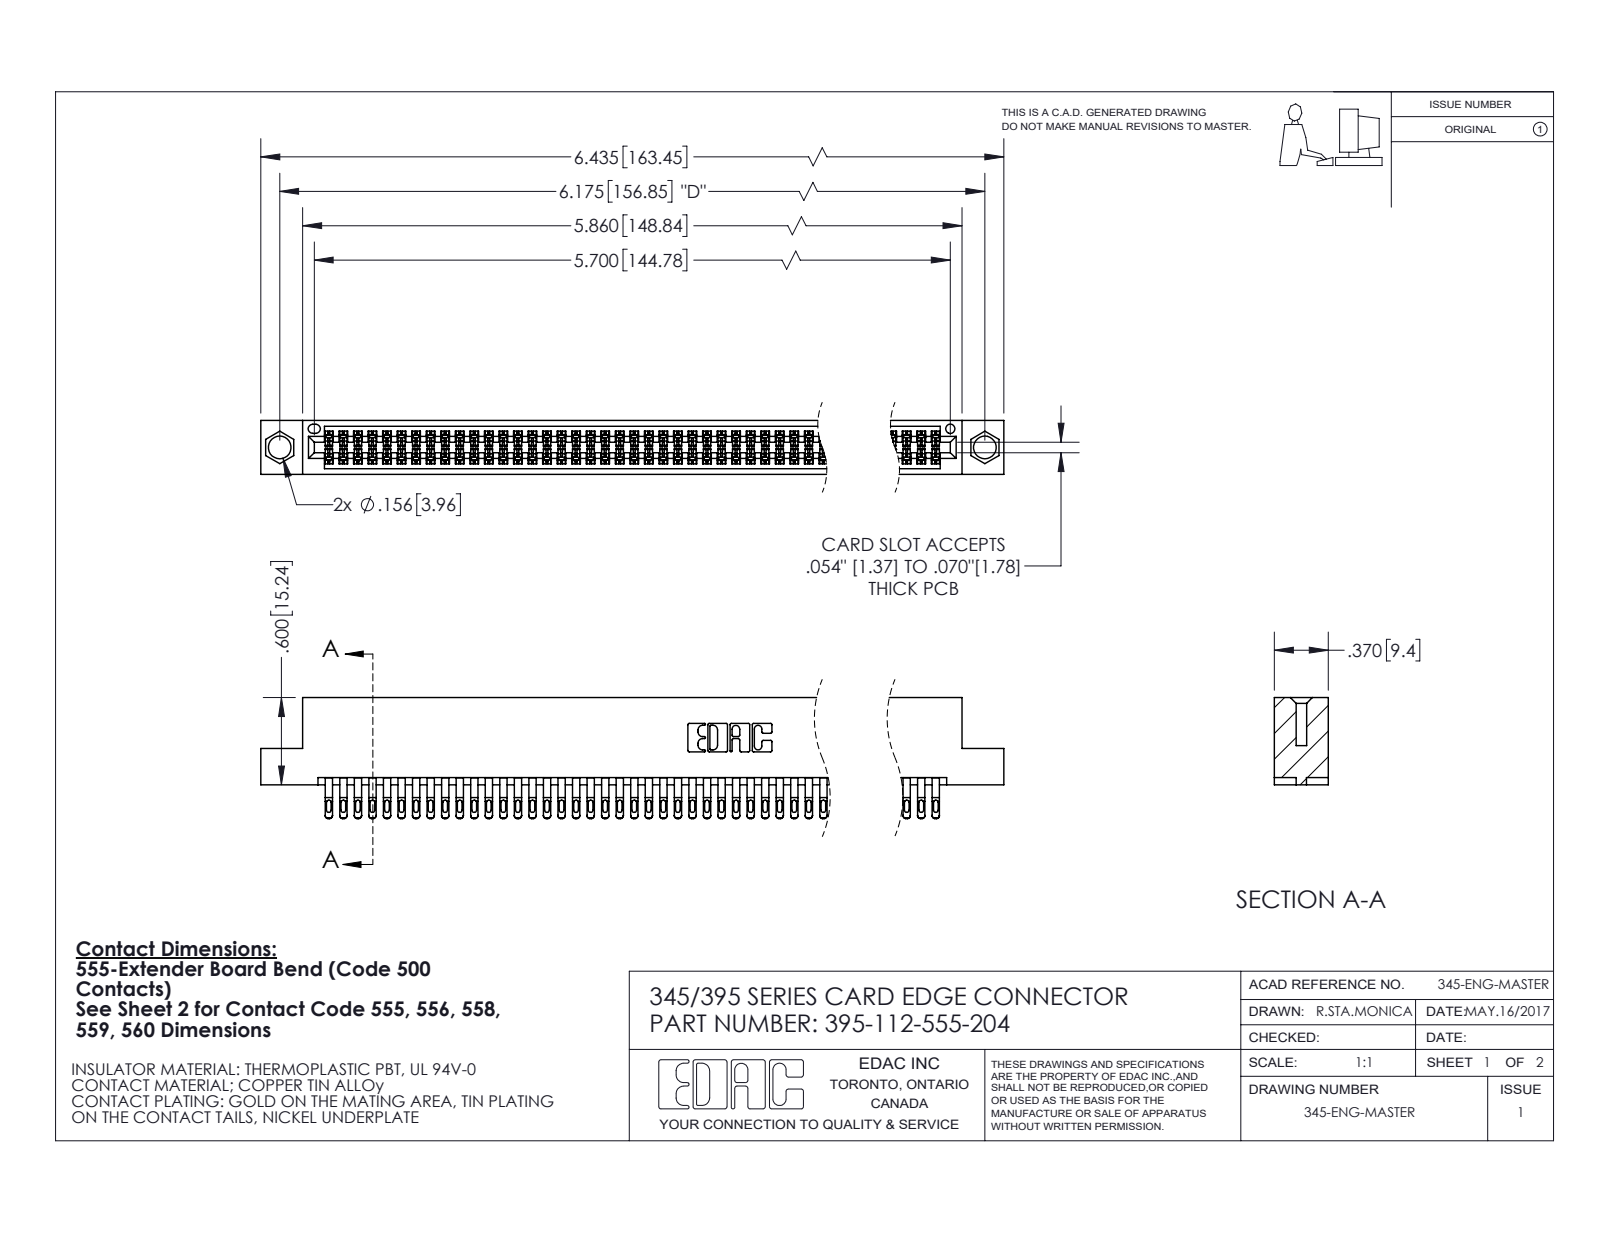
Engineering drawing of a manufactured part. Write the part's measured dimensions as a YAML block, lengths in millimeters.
part_name: "395-112-555-204; 345 Part_Flush Mounting Lugs - 0.156 Dia-TI; 345-292-001_555 Tail"
step_written_by: "SolidWorks 2020 (CONFIG_CONTROL_DESIGN)"
units: millimeters
bodies: {solids: 113, faces: 6412, planar: 3566, cylindrical: 2846, other: 0}
overall_size: [163.4, 21.1, 9.4]
volume: 16200
surface_area: 25240
round_holes:
  - {diameter: 4, count: 2}
  - {diameter: 1.6, count: 1}
partial_cylinders:
  - {radius: 0.4, count: 280}
  - {radius: 0.2, count: 224}
  - {radius: 0.5, count: 224}
  - {radius: 0.3, count: 22}
  - {radius: 0.2, count: 6}
  - {radius: 0.8, count: 6}
  - {radius: 0.7, count: 3}
  - {radius: 0.3, count: 2}
face_to_face_distances: [7.6, 1.8, 0.6, 9.4, 5.1, 2.5, 6.9, 5.7, 4.4, 3.8]
hole_center_spacings: [6.9, 150.9, 156.8]
